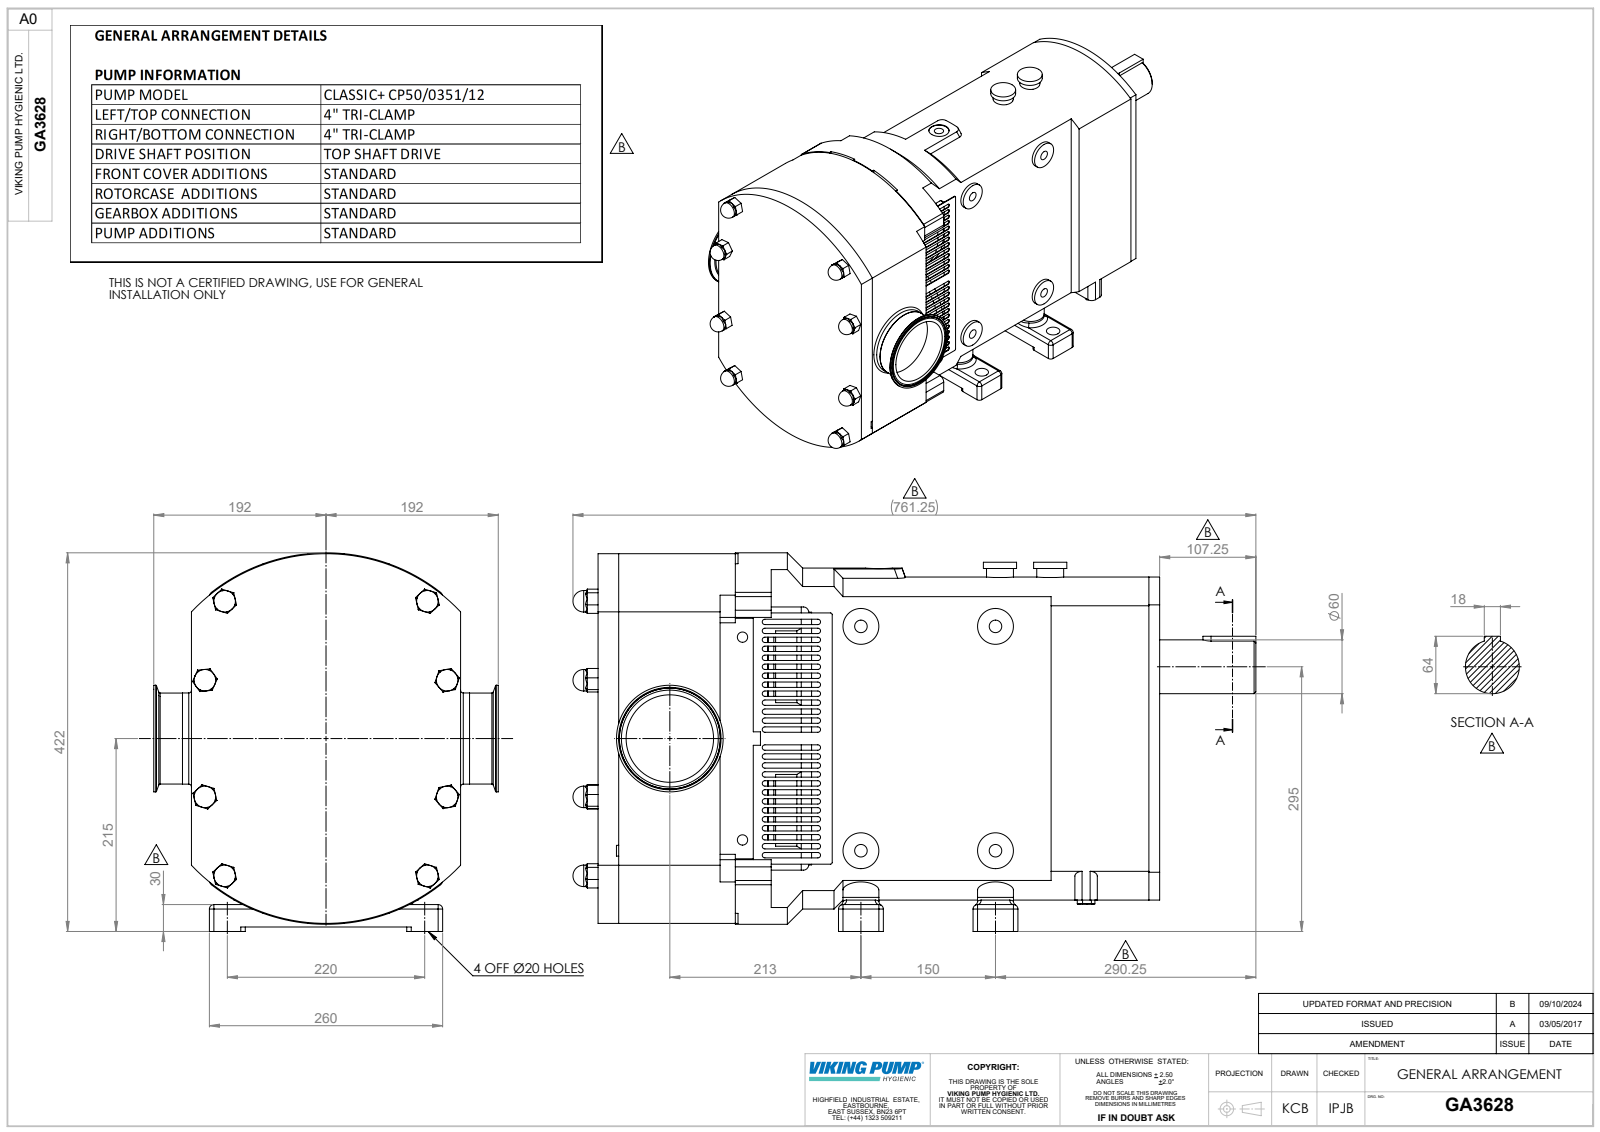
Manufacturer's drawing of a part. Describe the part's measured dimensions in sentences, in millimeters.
The part is named "Copy of Z94-5121-66 - 4 INCH^GA3628; GA3628; Copy of CP50S-0351 H TSD^GA3628". Its 3-D file was written by "SolidWorks 2023 (AUTOMOTIVE_DESIGN)". It is 3 solids with 1132 faces: 488 planar, 371 cylindrical and 273 other. Overall it measures 761.25 by 422 by 384 millimeters. Its volume is 45 400 000 cubic millimeters and its surface area 1 338 000 square millimeters. Round holes: 4 of diameter 14, 4 of diameter 20, 2 of diameter 11.5, 2 of diameter 35, 1 of diameter 13.84, 1 of diameter 30, 1 of diameter 97.5. Round bosses or shafts: 8 of diameter 40, 8 of diameter 24, 2 of diameter 169, 2 of diameter 80, 2 of diameter 70, 2 of diameter 68, 2 of diameter 37, 2 of diameter 31.75. Partial cylindrical surfaces (rounded edges, fillets, slot ends): 52 of radius 3, 36 of radius 5, 14 of radius 6, 12 of radius 8, 4 of radius 2, 1 of radius 9, 1 of radius 154.5, 1 of radius 165. The main face-to-face distances are 172, 626, 188.5, 16.5, 47.5, 64, 236, 252.5, 136, 490. The hole center spacings are 150, 110.11, 111.8, 125.78, 132.54, 139.03, 170.29, 190.07.
